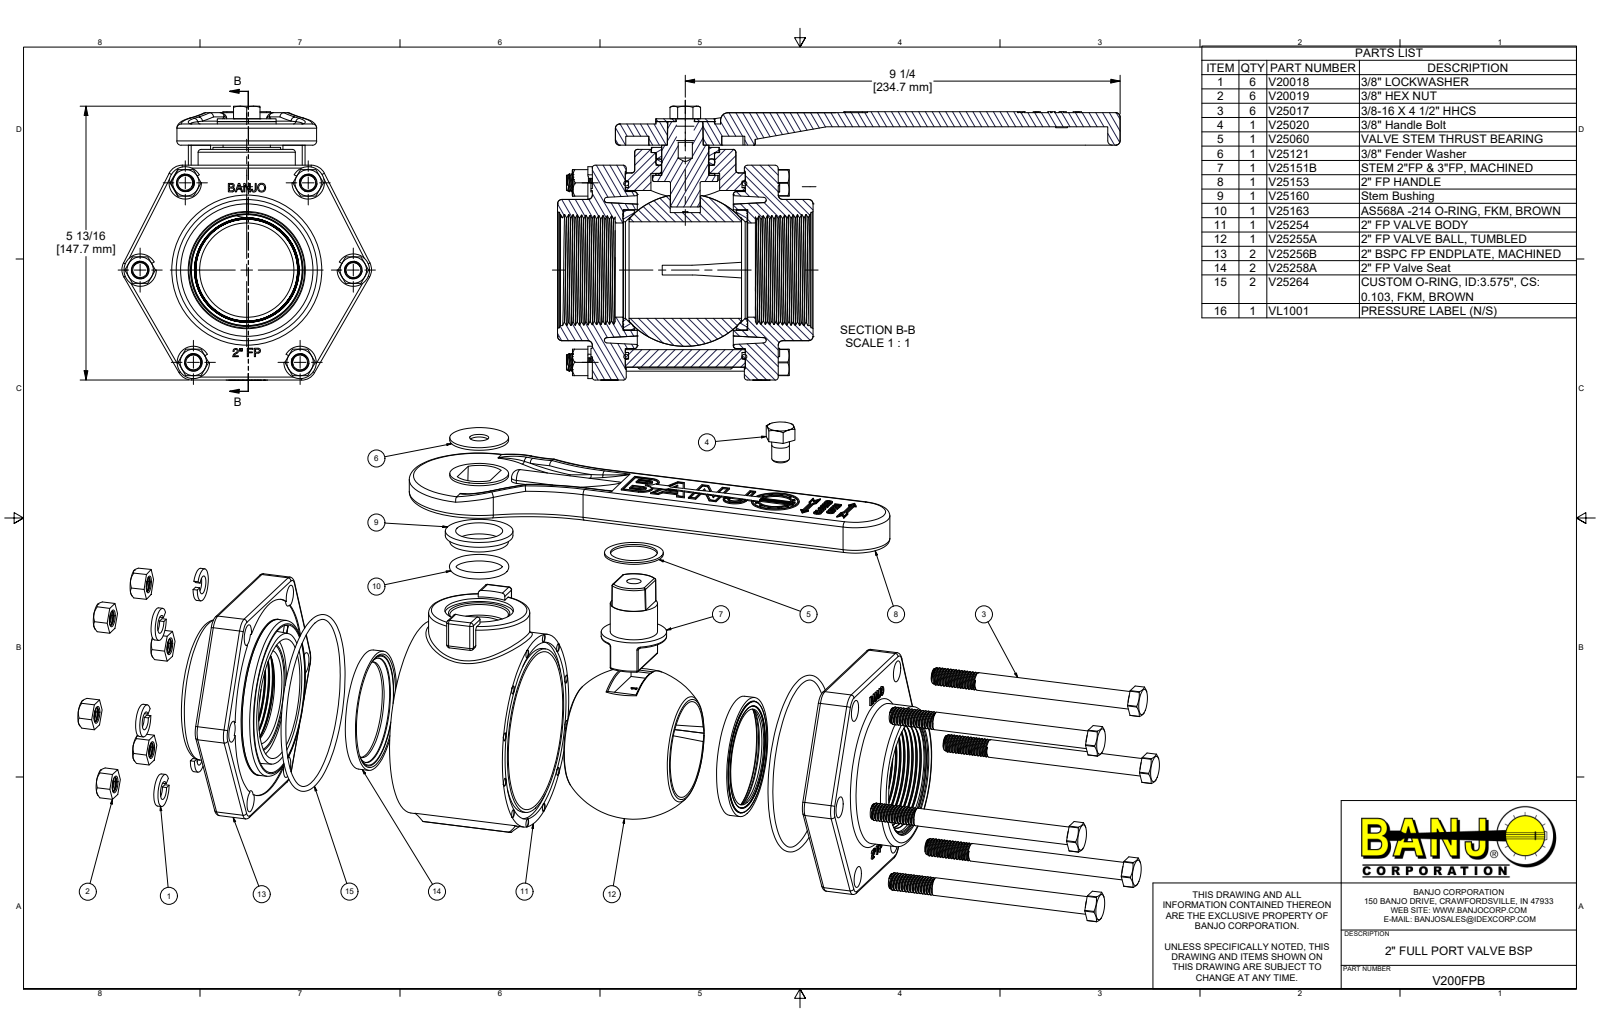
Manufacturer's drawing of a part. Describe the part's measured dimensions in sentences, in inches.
The part is named "V200FPB; V20018; V20019; V25017 (+8 more)". Its 3-D file was written by "Autodesk Inventor 2018 (AUTOMOTIVE_DESIGN)". It is 36 solids with 3465 faces: 1705 planar, 622 cylindrical and 1138 other. Overall it measures 11.955 by 5.82 by 5.306 inches. Its volume is 58.3 cubic inches and its surface area 453.5 square inches. Round holes: 12 of diameter 0.17, 6 of diameter 0.307, 6 of diameter 0.385, 6 of diameter 0.45, 1 of diameter 0.307, 1 of diameter 0.375, 1 of diameter 0.406, 1 of diameter 0.681, 1 of diameter 0.962, 1 of diameter 1, 1 of diameter 1.016, 1 of diameter 1.245. Round bosses or shafts: 90 of diameter 0.324, 7 of diameter 0.375, 6 of diameter 0.687, 1 of diameter 3.5, 1 of diameter 3.342, 1 of diameter 3.335, 1 of diameter 3, 1 of diameter 2.969. Partial cylindrical surfaces (rounded edges, fillets, slot ends): 32 of radius 0.06, 24 of radius 0.062, 12 of radius 0.162, 10 of radius 0.032, 8 of radius 0.09, 6 of radius 0.156, 6 of radius 0.313, 6 of radius 0.32. The main face-to-face distances are 3.25, 0.7, 0.05, 2.53, 3.95, 0.07, 2.55, 0.26, 0.02, 0.72. The hole center spacings are 1.977, 2.796, 3.82, 1.023, 3.424, 3.921, 3.954, 0.623.
